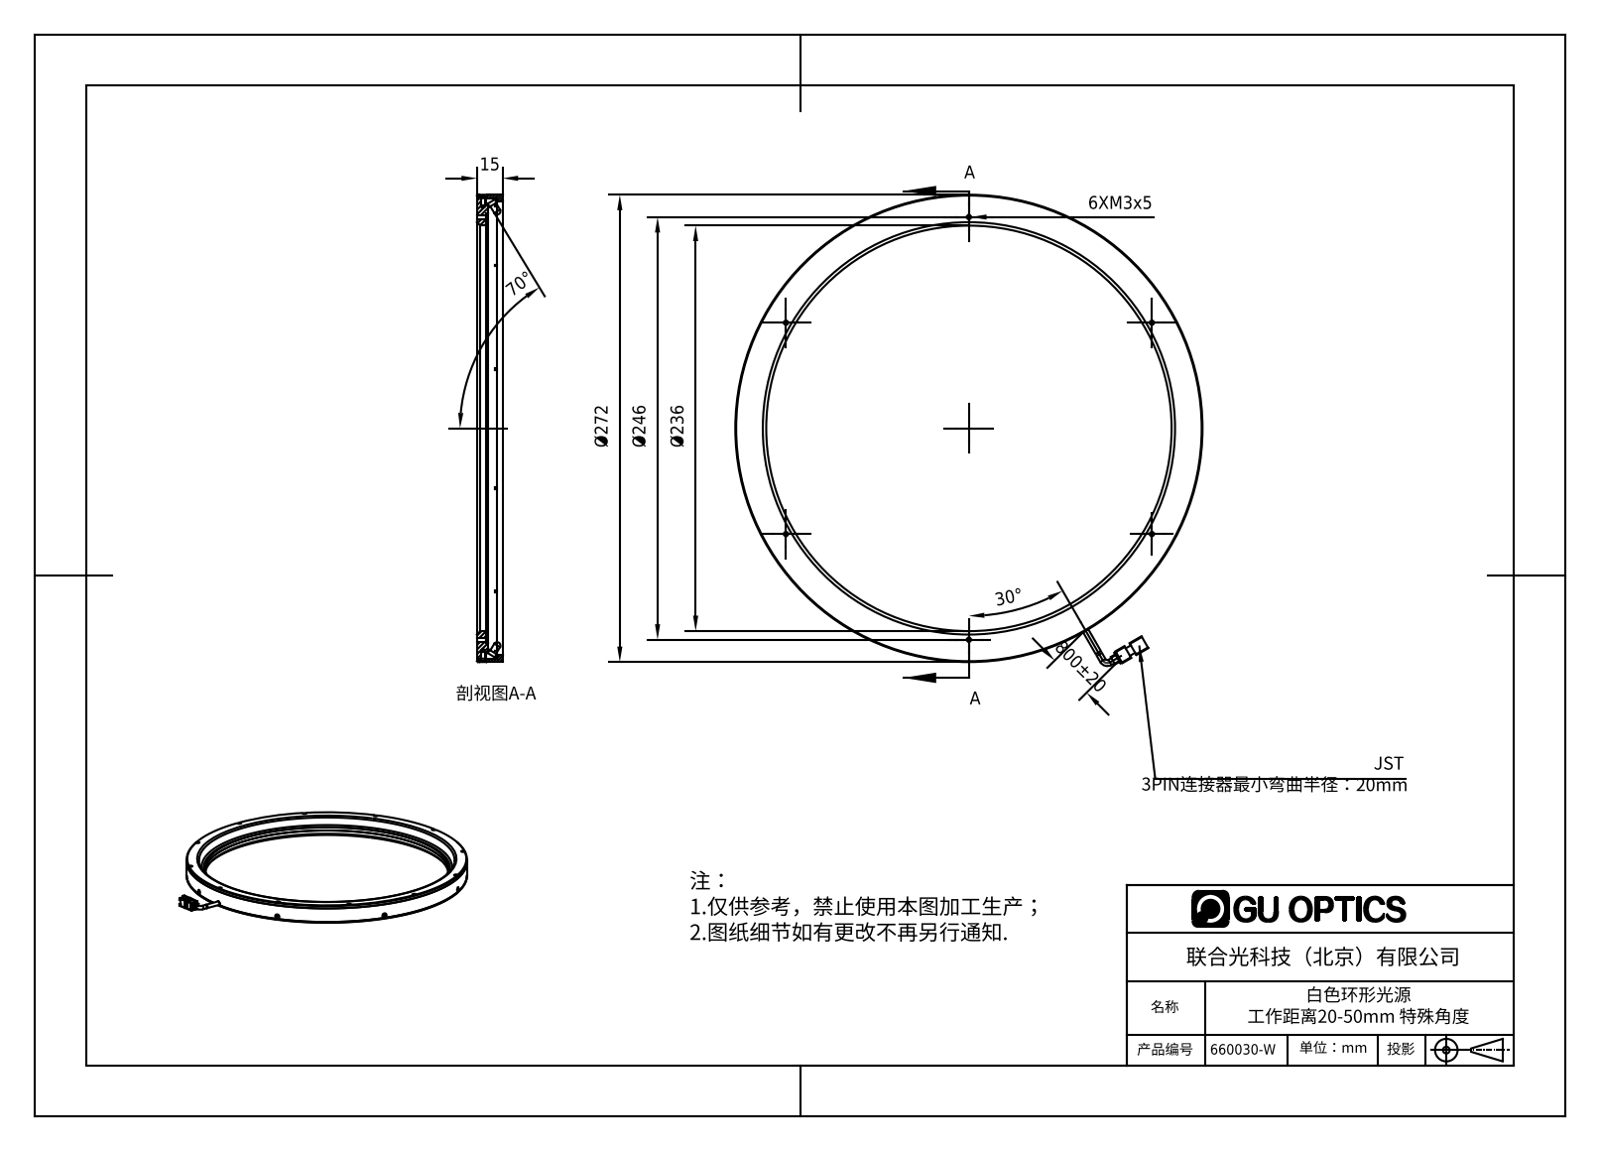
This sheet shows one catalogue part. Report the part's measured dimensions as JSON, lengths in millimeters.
{"part_name": "660030-W", "step_written_by": "SolidWorks 2016 (AUTOMOTIVE_DESIGN)", "units": "millimeters", "bodies": {"solids": 156, "faces": 2958, "planar": 1895, "cylindrical": 793, "other": 270}, "overall_size": [274.35, 272, 19.24], "volume_mm3": 168197, "surface_area_mm2": 140450, "round_holes": [[1.6, 18], [1.25, 12], [1.7, 12], [2, 6], [2.4, 6], [2.5, 6], [3.5, 1], [236, 1], [250, 1], [264, 1]], "round_bosses_or_shafts": [[3.8, 150], [3, 150], [3.5, 2], [272, 1], [268, 1], [260, 1]], "partial_cylinders_radius": [[0.5, 8], [1, 4], [1.6, 1], [3, 1]], "face_to_face_distances": [14.94, 3, 17.94, 5.3, 9.64, 12.64, 6.5, 8.44, 1, 1.2], "hole_center_spacings": [134, 34.98, 163.15, 247.6, 265.71, 69.36, 102.56, 258.87]}
